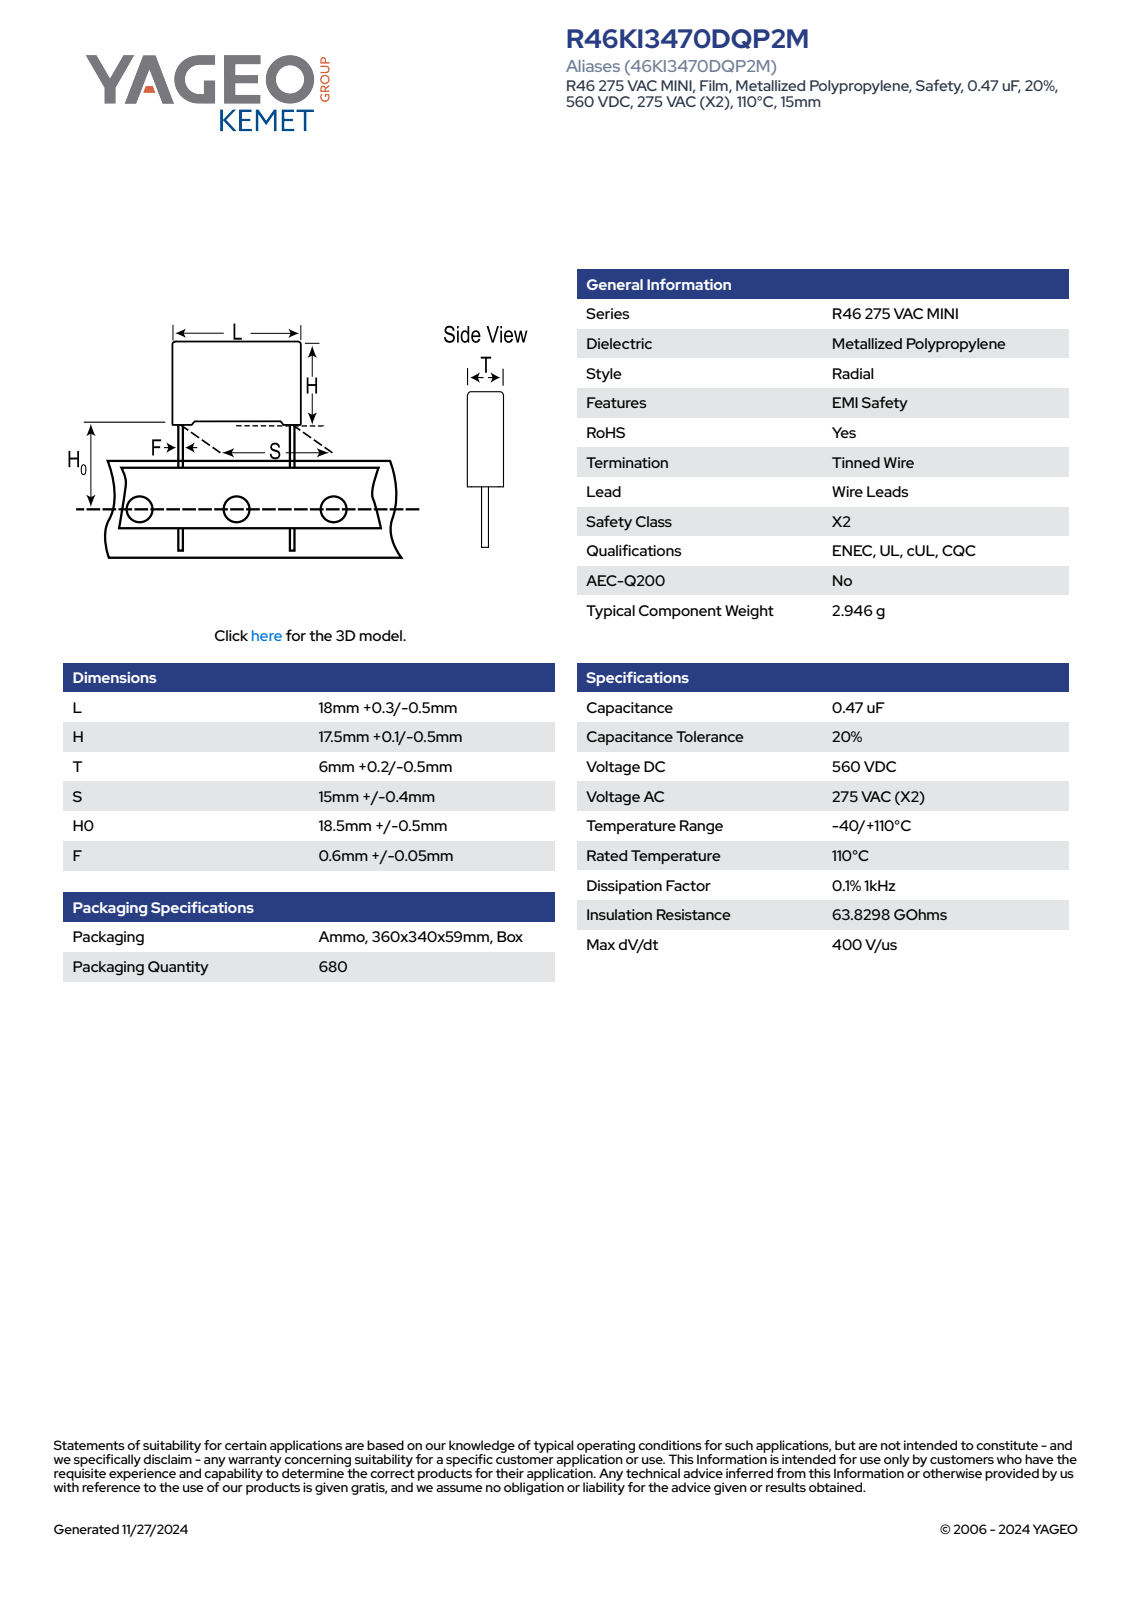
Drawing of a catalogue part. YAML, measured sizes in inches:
part_name: "CFR_RB2_18X17.5X6_L18.3H17.6T6.2S15H019F0.65"
step_written_by: "SolidWorks 2020 (AUTOMOTIVE_DESIGN)"
units: inches
bodies: {solids: 4, faces: 85, planar: 77, cylindrical: 8, other: 0}
overall_size: [1.441, 0.72, 0.244]
volume: 0.118
surface_area: 1.845
round_bosses_or_shafts:
  - {diameter: 0.026, count: 2}
partial_cylinders:
  - {radius: 0.02, count: 4}
face_to_face_distances: [0.244, 0.72, 0.663, 0.024, 0.03, 0.693, 0.669, 0.22, 0.696, 0.196]
